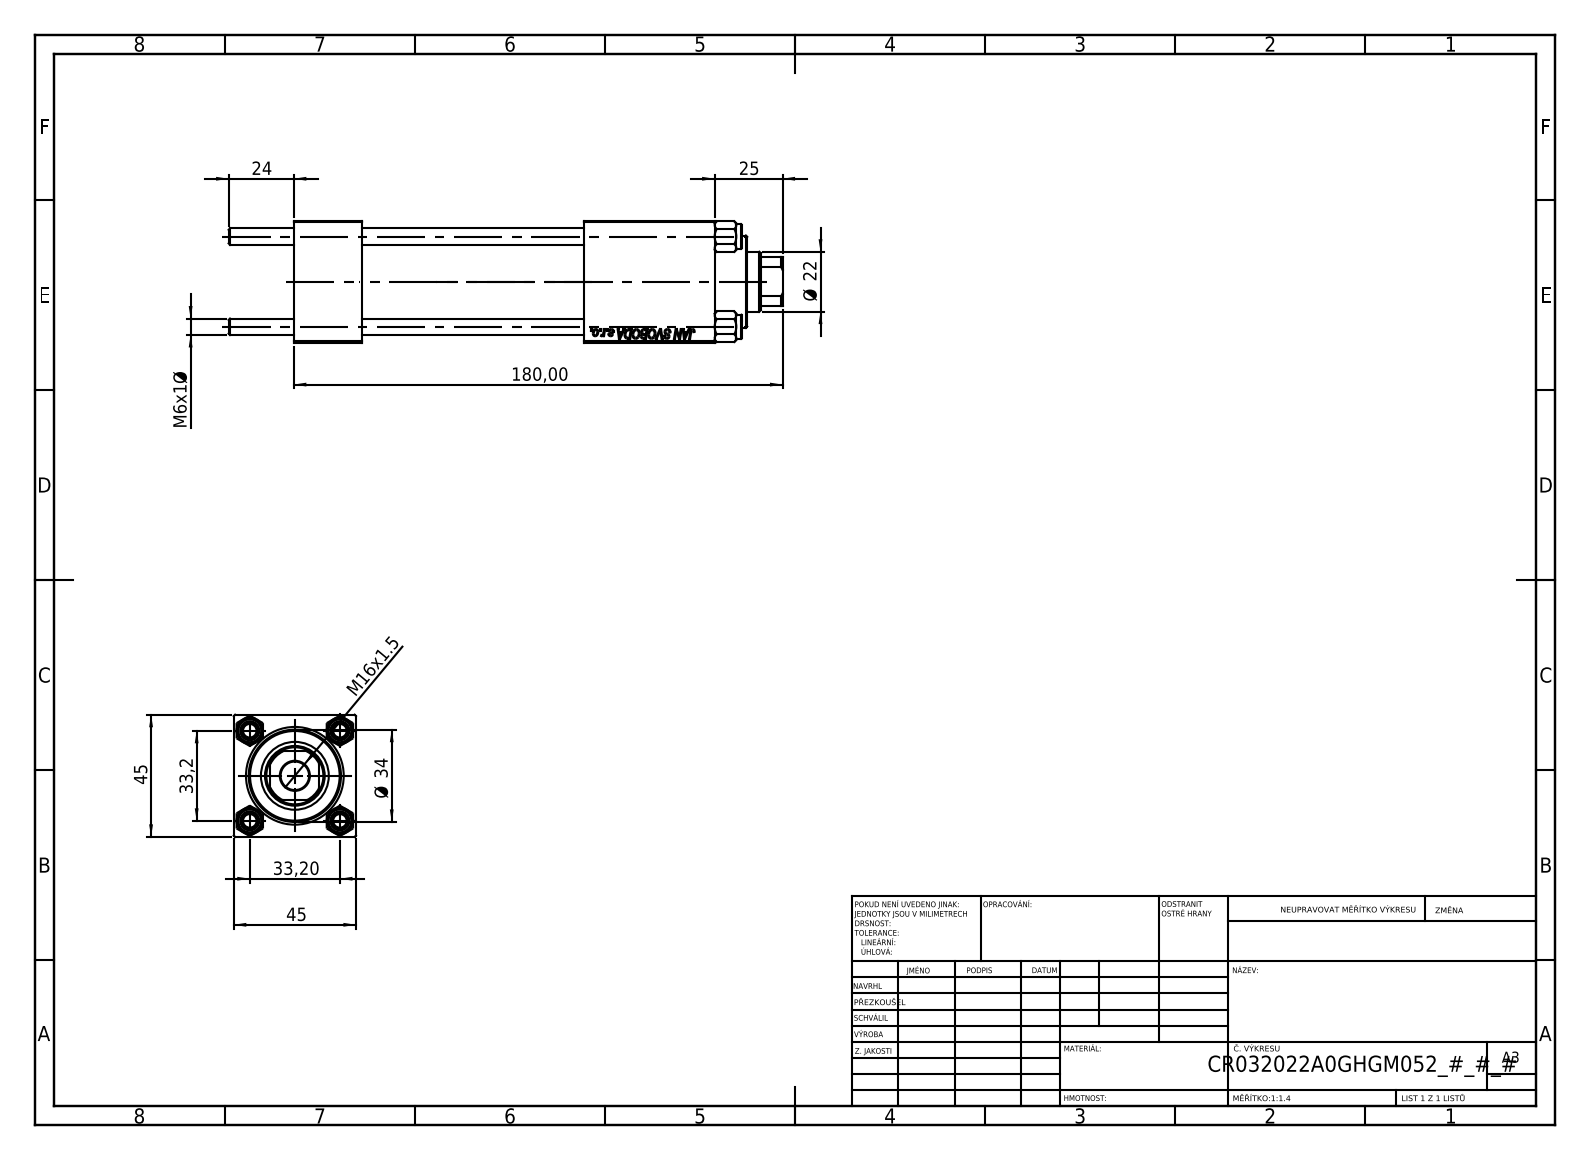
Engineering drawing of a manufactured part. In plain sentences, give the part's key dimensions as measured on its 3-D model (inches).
The part is named "V215CR_BODY_A; NUT_M5; V215_VC_A; CR025_012_A_0_G_A_G_M_020_+#_##_TYCINKA (+1 more)". Its 3-D file was written by "SolidWorks 2019 (CONFIG_CONTROL_DESIGN)". It is 11 solids with 1133 faces: 519 planar, 78 cylindrical and 536 other. Overall it measures 8.031 by 1.772 by 1.772 inches. Its volume is 14.68 cubic inches and its surface area 137.5 square inches. Round holes: 4 of diameter 0.236, 2 of diameter 0.276, 2 of diameter 0.518, 2 of diameter 0.787, 1 of diameter 0.413, 1 of diameter 0.866, 1 of diameter 0.945, 1 of diameter 0.984, 1 of diameter 1.26, 1 of diameter 1.299. Round bosses or shafts: 4 of diameter 0.354, 1 of diameter 1.496, 1 of diameter 1.339. Partial cylindrical surfaces (rounded edges, fillets, slot ends): 1 of radius 0.413. The main face-to-face distances are 1.772, 0.984, 6.102, 4.213, 3.228, 5.118, 1.89, 4.972, 3.988, 0.76. The hole center spacings are 0.924, 1.307, 1.848, 4.232.
